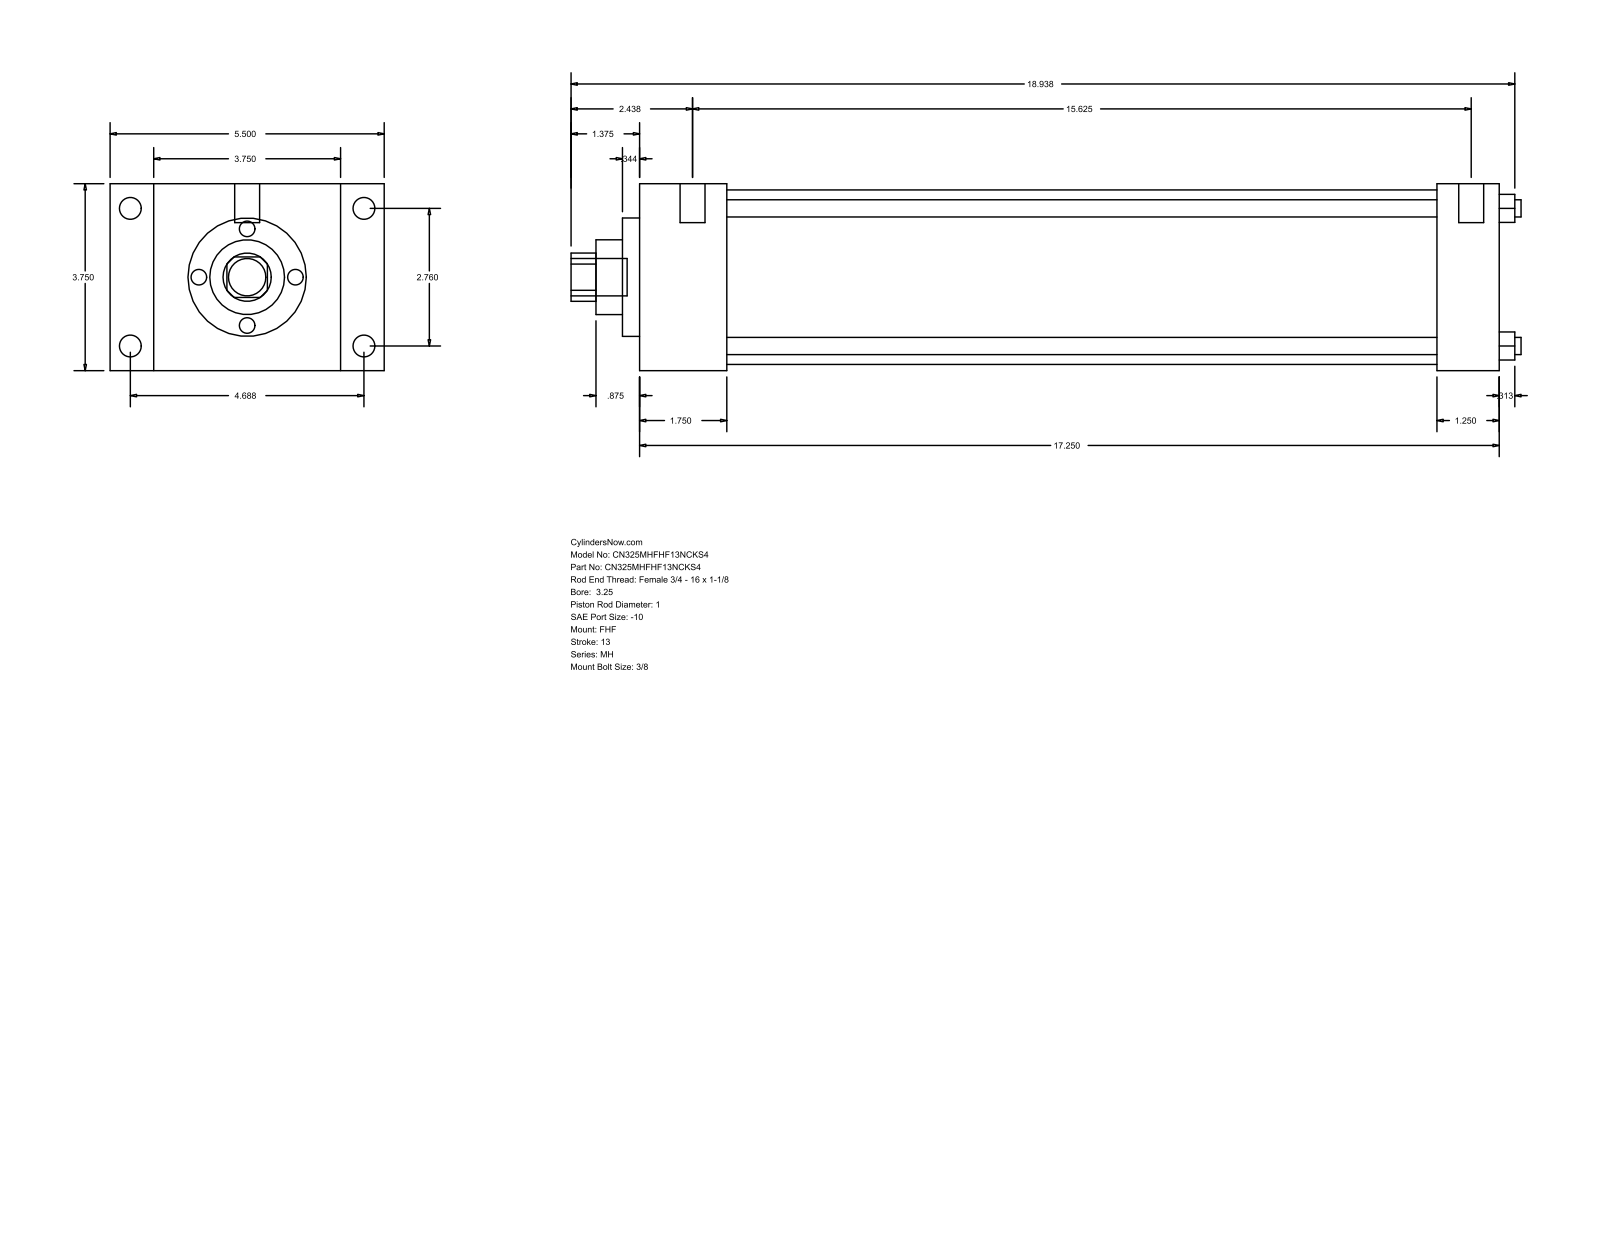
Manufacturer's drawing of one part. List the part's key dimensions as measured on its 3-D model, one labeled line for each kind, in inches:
Part name (STEP PRODUCT): MH_FHF__0325_1
STEP written by: GSSL Pune (CONFIG_CONTROL_DESIGN)
Units: inches
Bodies: 0 solids, 90 faces (61 planar, 29 cylindrical, 0 other)
Overall size (bounding box): 19.063 × 5.5 × 3.75
Round holes (diameter × count): ⌀0.345 ×4, ⌀1 ×1, ⌀1.5 ×1, ⌀2.375 ×1, ⌀3.5 ×1
Round bosses / shafts (diameter × count): ⌀0.438 ×4, ⌀0.219 ×4, ⌀0.5 ×2, ⌀0.75 ×1
Partial cylindrical surfaces — rounded edges, fillets, slot ends (radius × count): R0.484 ×1
Main face-to-face distances: 3.75, 17.25, 1.75, 15.5, 0.875, 4.625, 5.5, 16, 14.25, 1.25
Hole centre spacings: 1.952, 2.76, 3.903
